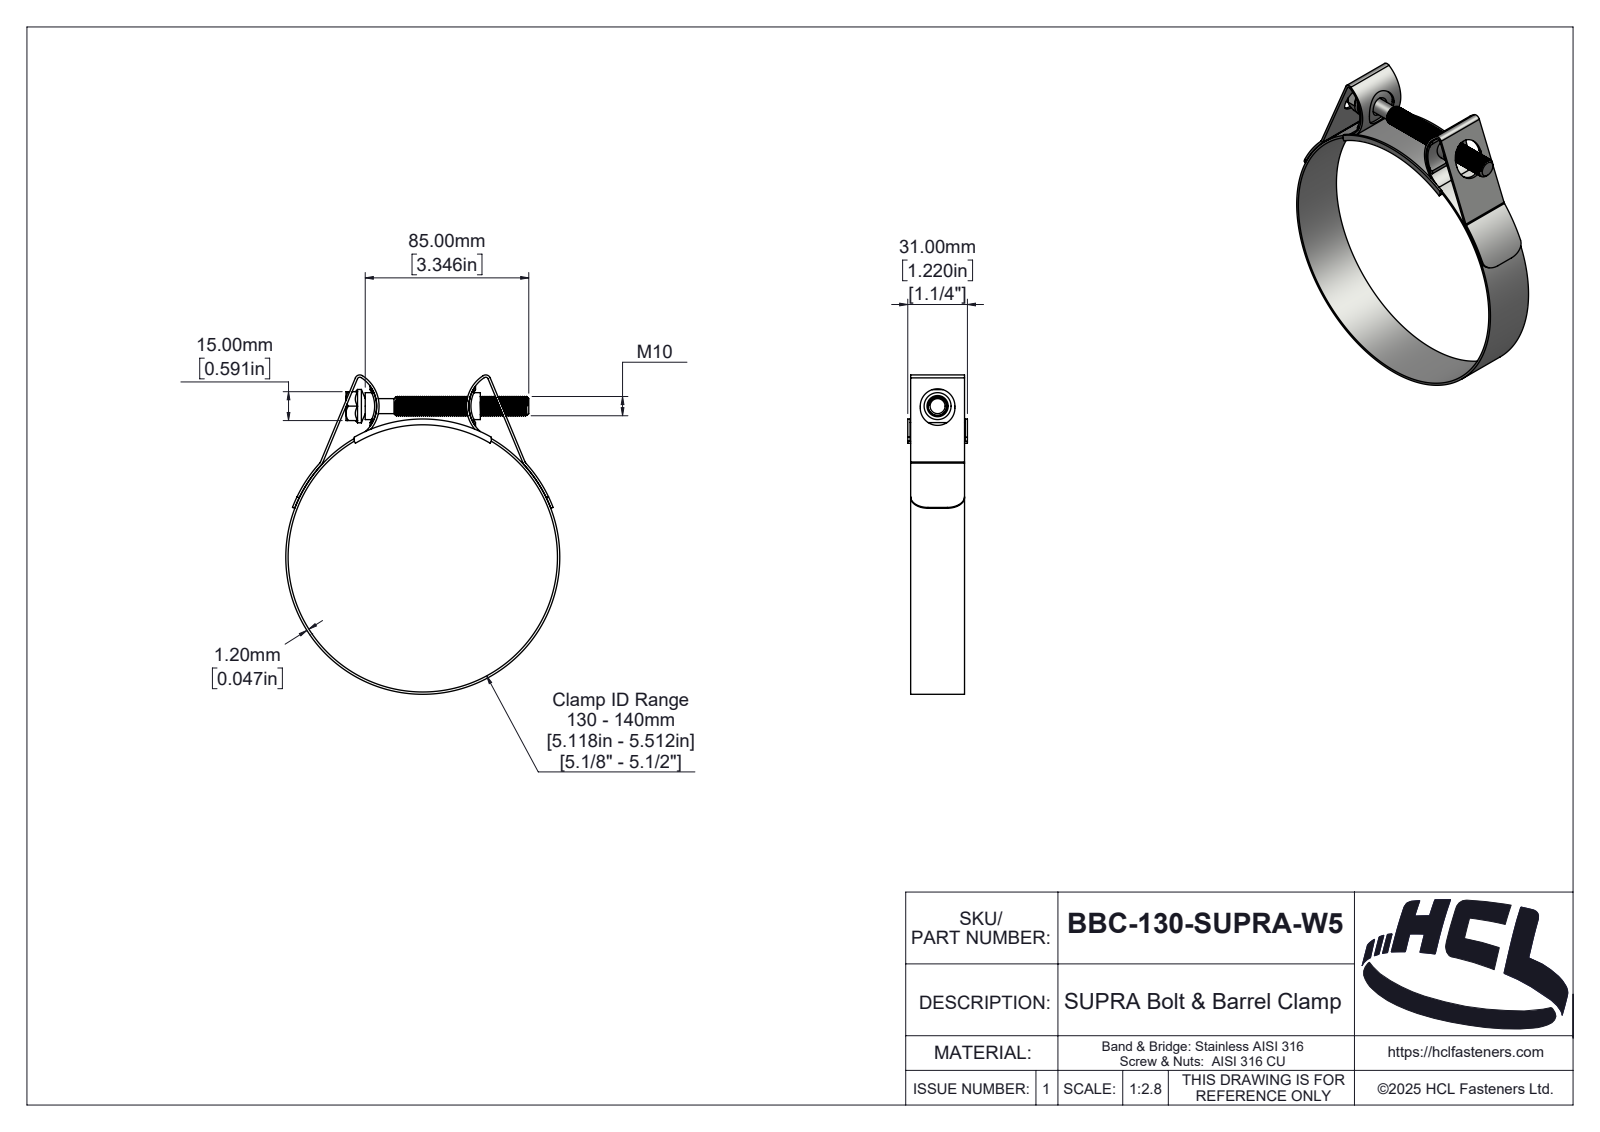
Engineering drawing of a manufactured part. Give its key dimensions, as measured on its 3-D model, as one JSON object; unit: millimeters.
{"part_name": "BBC-130-SUPRA-W5", "step_written_by": "SolidWorks 2025 (AUTOMOTIVE_DESIGN)", "units": "millimeters", "bodies": {"solids": 5, "faces": 382, "planar": 46, "cylindrical": 249, "other": 87}, "overall_size": [165.9, 142.4, 31], "volume_mm3": 31247, "surface_area_mm2": 46325, "round_holes": [[140, 1]], "round_bosses_or_shafts": [[142.4, 1], [17.32, 1], [14, 1], [10, 1], [7.8, 1]], "partial_cylinders_radius": [[1, 4], [1.3, 2], [2, 2], [2.5, 2], [3.2, 2], [9, 2], [16.49, 2], [17.49, 2]], "face_to_face_distances": [1.2, 28, 1.5, 29.5, 29.8, 28.3, 31, 28.6, 15, 2.5]}
